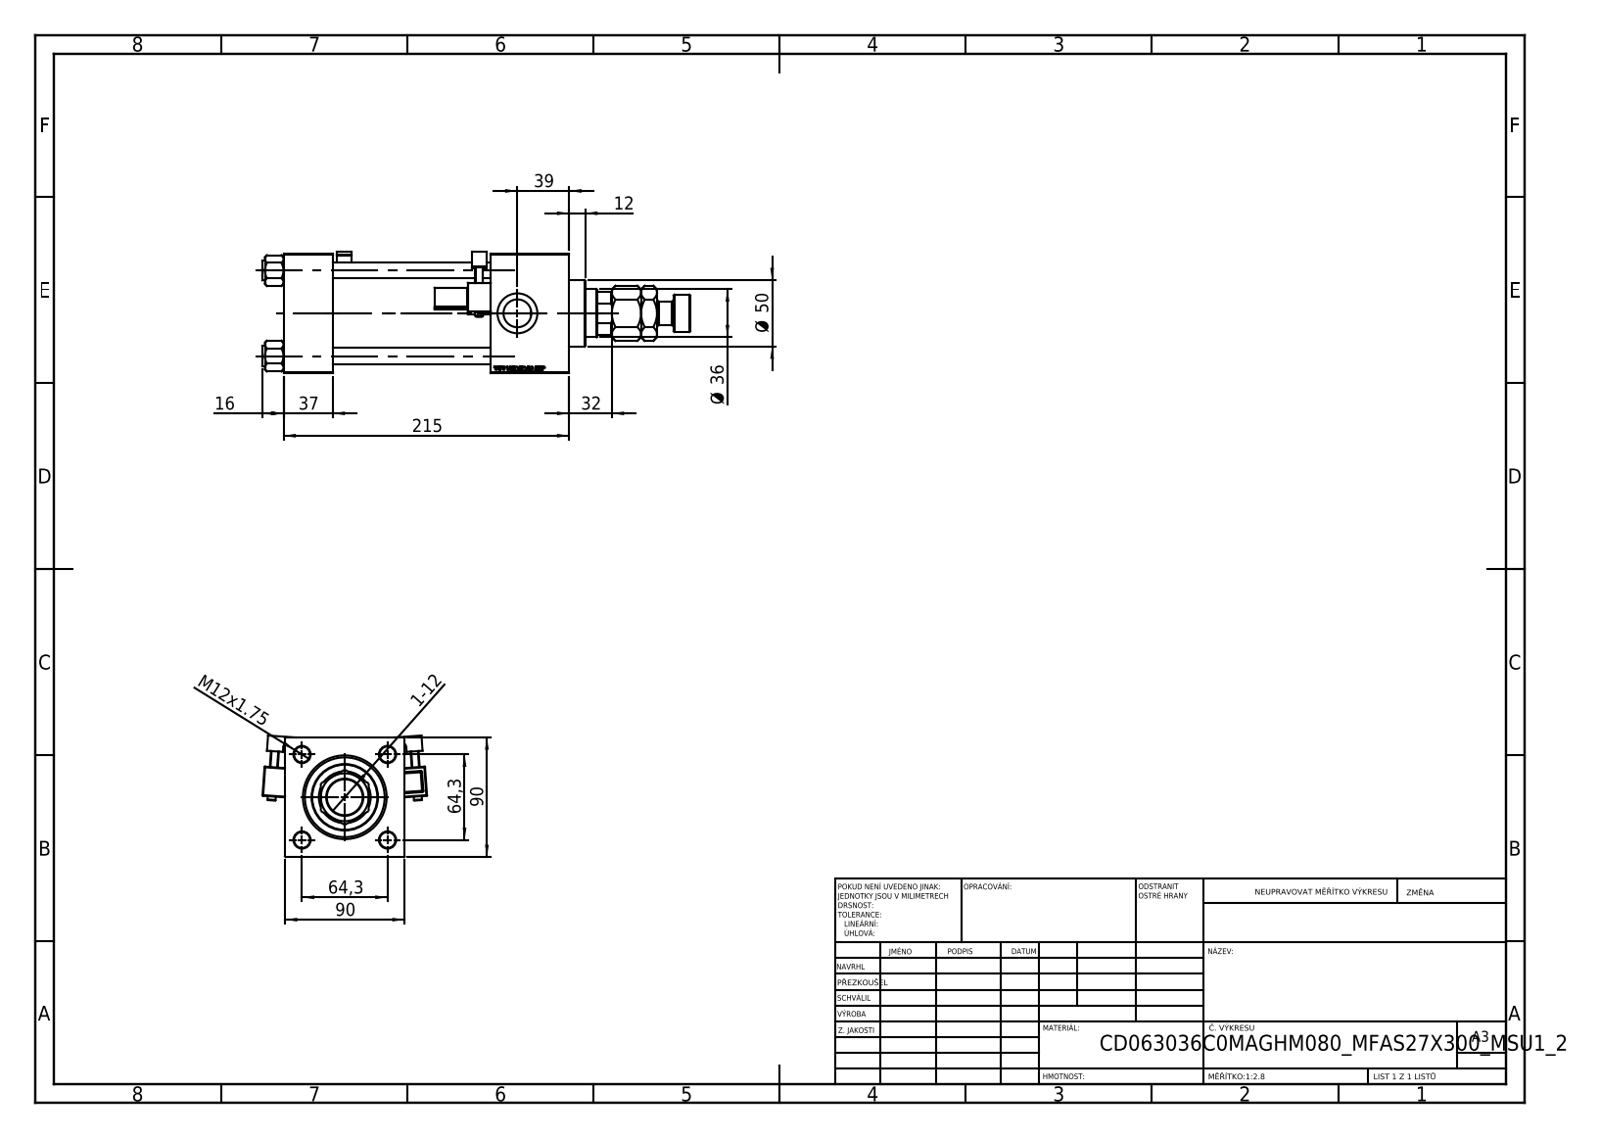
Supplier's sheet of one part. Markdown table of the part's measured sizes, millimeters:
| quantity | value |
| --- | --- |
| part name | V215CD_VC_C; V215CD_Body_C; V215CD_VCP_C; V215CD_C_TYCINKA (+3 more) |
| STEP written by | SolidWorks 2019 (CONFIG_CONTROL_DESIGN) |
| units | millimeters |
| bodies | 14 solids, 1355 faces (600 planar, 151 cylindrical, 604 other) |
| overall size | 322 × 123.72 × 91.43 |
| volume | 1 183 000 mm³ |
| surface area | 246 018 mm² |
| round holes (diameter × count) | 12 × 4, 7 × 2, 20.96 × 2, 30 × 2, 25.5 × 1, 36 × 1, 39 × 1, 50 × 1, 60 × 1, 63 × 1 |
| round bosses / shafts (diameter × count) | 15 × 4, 6 × 2, 69 × 1, 28 × 1, 18 × 1 |
| partial cylindrical surfaces (radius × count) | 0.5 × 48, 1 × 2, 2.5 × 2, 4 × 2, 17.5 × 1 |
| main face-to-face distances | 90, 37, 59, 156, 119, 215, 178, 186.3, 149.3, 30.3 |
| hole center spacings | 45.47, 64.3, 90.93 |
